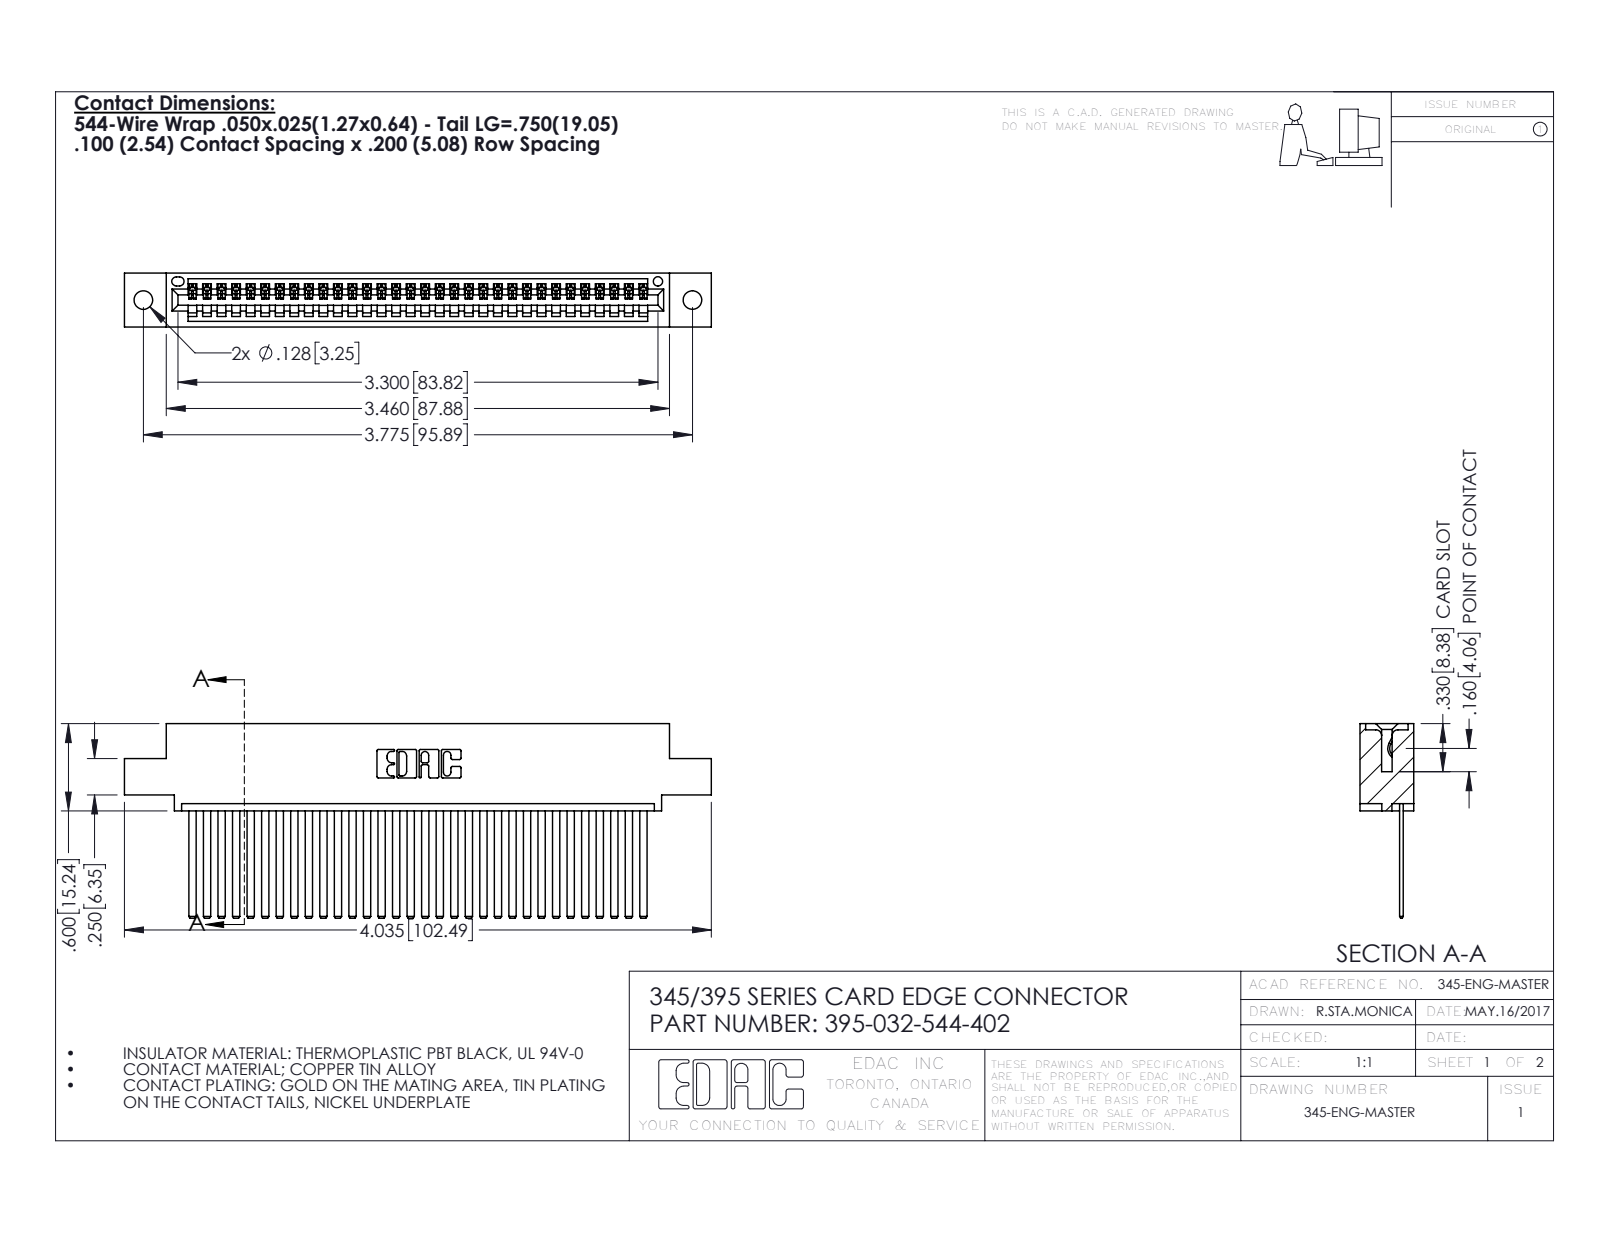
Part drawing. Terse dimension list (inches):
name: 345 Part_0.110 Offset - 0.128 Dia; 345-292-001_345-293-144; 395-032-544-402
written by: SolidWorks 2016 (CONFIG_CONTROL_DESIGN)
unit: in
bodies: 33 solids, 1794 faces (1236 planar, 558 cylindrical, 0 other)
size: 4.035 × 1.337 × 0.37
volume: 0.605 in³; area: 21.64 in²
holes: 2× ⌀0.128, 1× ⌀0.064
rounds: 64× R0.006, 22× R0.01, 6× R0.007, 6× R0.031, 3× R0.026, 2× R0.031, 2× R0.04, 1× R0.014
face distances: 0.072, 0.298, 0.025, 0.098, 0.272, 0.37, 0.2, 0.225, 0.149, 0.072
hole spacings: 0.27, 3.54, 3.775
